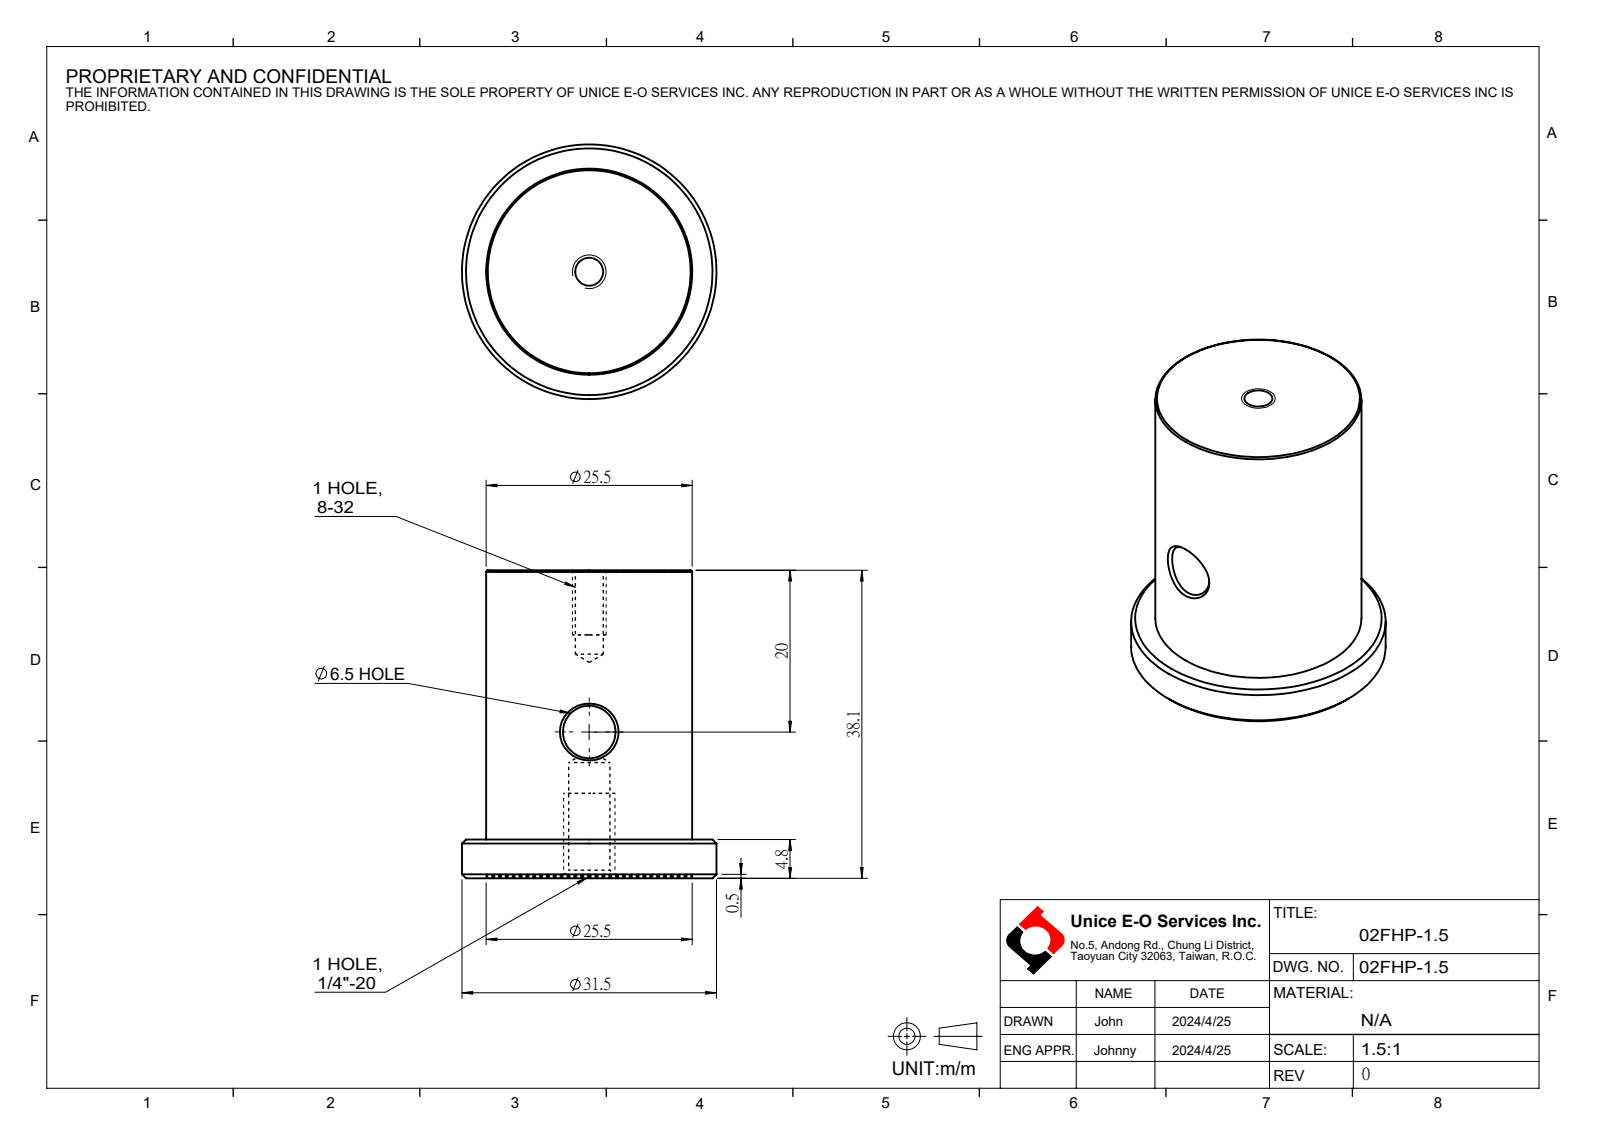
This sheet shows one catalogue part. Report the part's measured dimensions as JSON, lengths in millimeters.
{"part_name": "02FHP-1.5", "step_written_by": "SolidWorks 2020 (CONFIG_CONTROL_DESIGN)", "units": "millimeters", "bodies": {"solids": 1, "faces": 36, "planar": 4, "cylindrical": 12, "other": 20}, "overall_size": [38.1, 31.5, 31.5], "volume_mm3": 19231, "surface_area_mm2": 5421, "round_holes": [[3.45, 1], [5.11, 1], [6.5, 1], [25.5, 1]], "round_bosses_or_shafts": [[31.5, 1]], "face_to_face_distances": [37.6, 4.3, 33.3, 0.5, 4.8, 38.1]}
